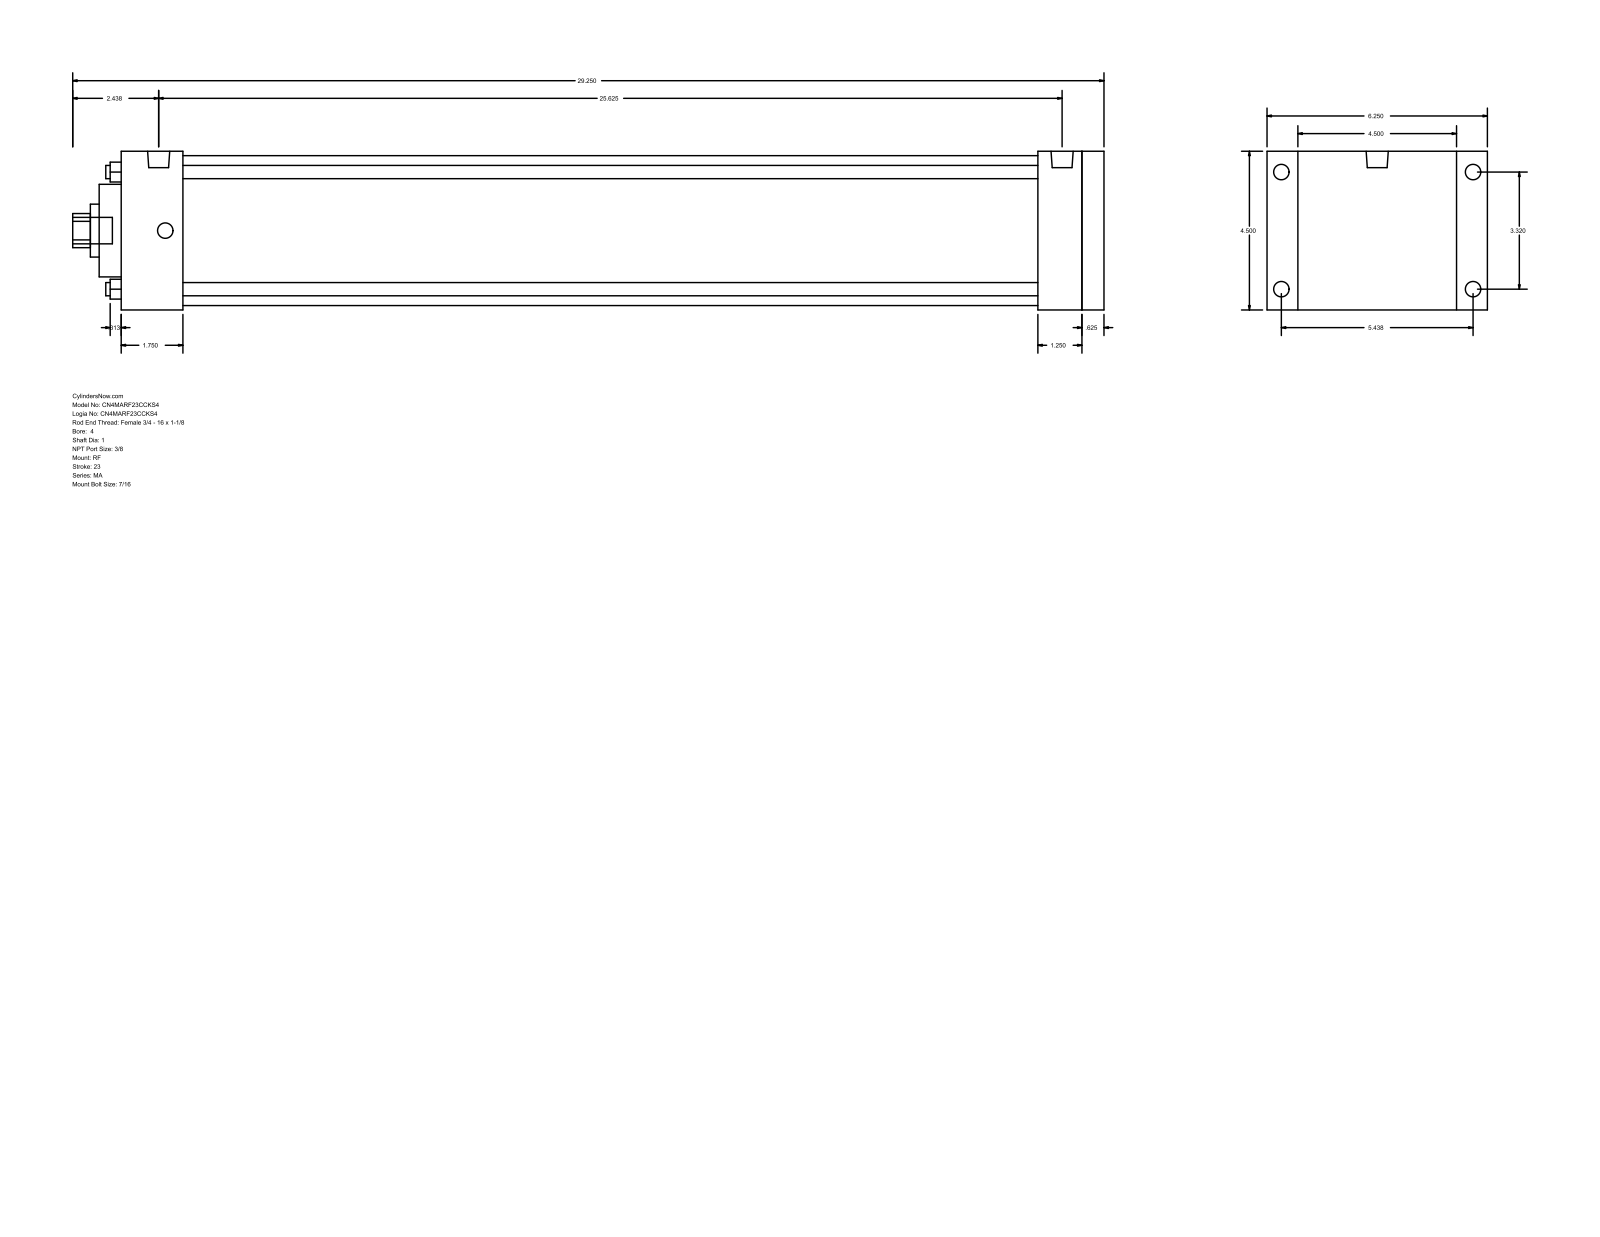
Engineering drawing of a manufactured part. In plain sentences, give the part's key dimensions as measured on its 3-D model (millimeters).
The part is named "MA_RF__0400_1". Its 3-D file was written by "GSSL Pune (CONFIG_CONTROL_DESIGN)". It is 0 solids with 94 faces: 65 planar, 29 cylindrical and 0 other. Overall it measures 742.95 by 158.75 by 114.3 millimeters. Round holes: 4 of diameter 9.53, 1 of diameter 25.4, 1 of diameter 38.1, 1 of diameter 66.67, 1 of diameter 107.95. Round bosses or shafts: 8 of diameter 11.11, 2 of diameter 15.93, 1 of diameter 19.05. Partial cylindrical surfaces (rounded edges, fillets, slot ends): 1 of radius 12.29. The main face-to-face distances are 114.3, 708.03, 15.87, 692.16, 22.23, 136.53, 660.41, 31.75, 47.62, 44.46. The hole center spacings are 59.62, 84.32, 119.25.
